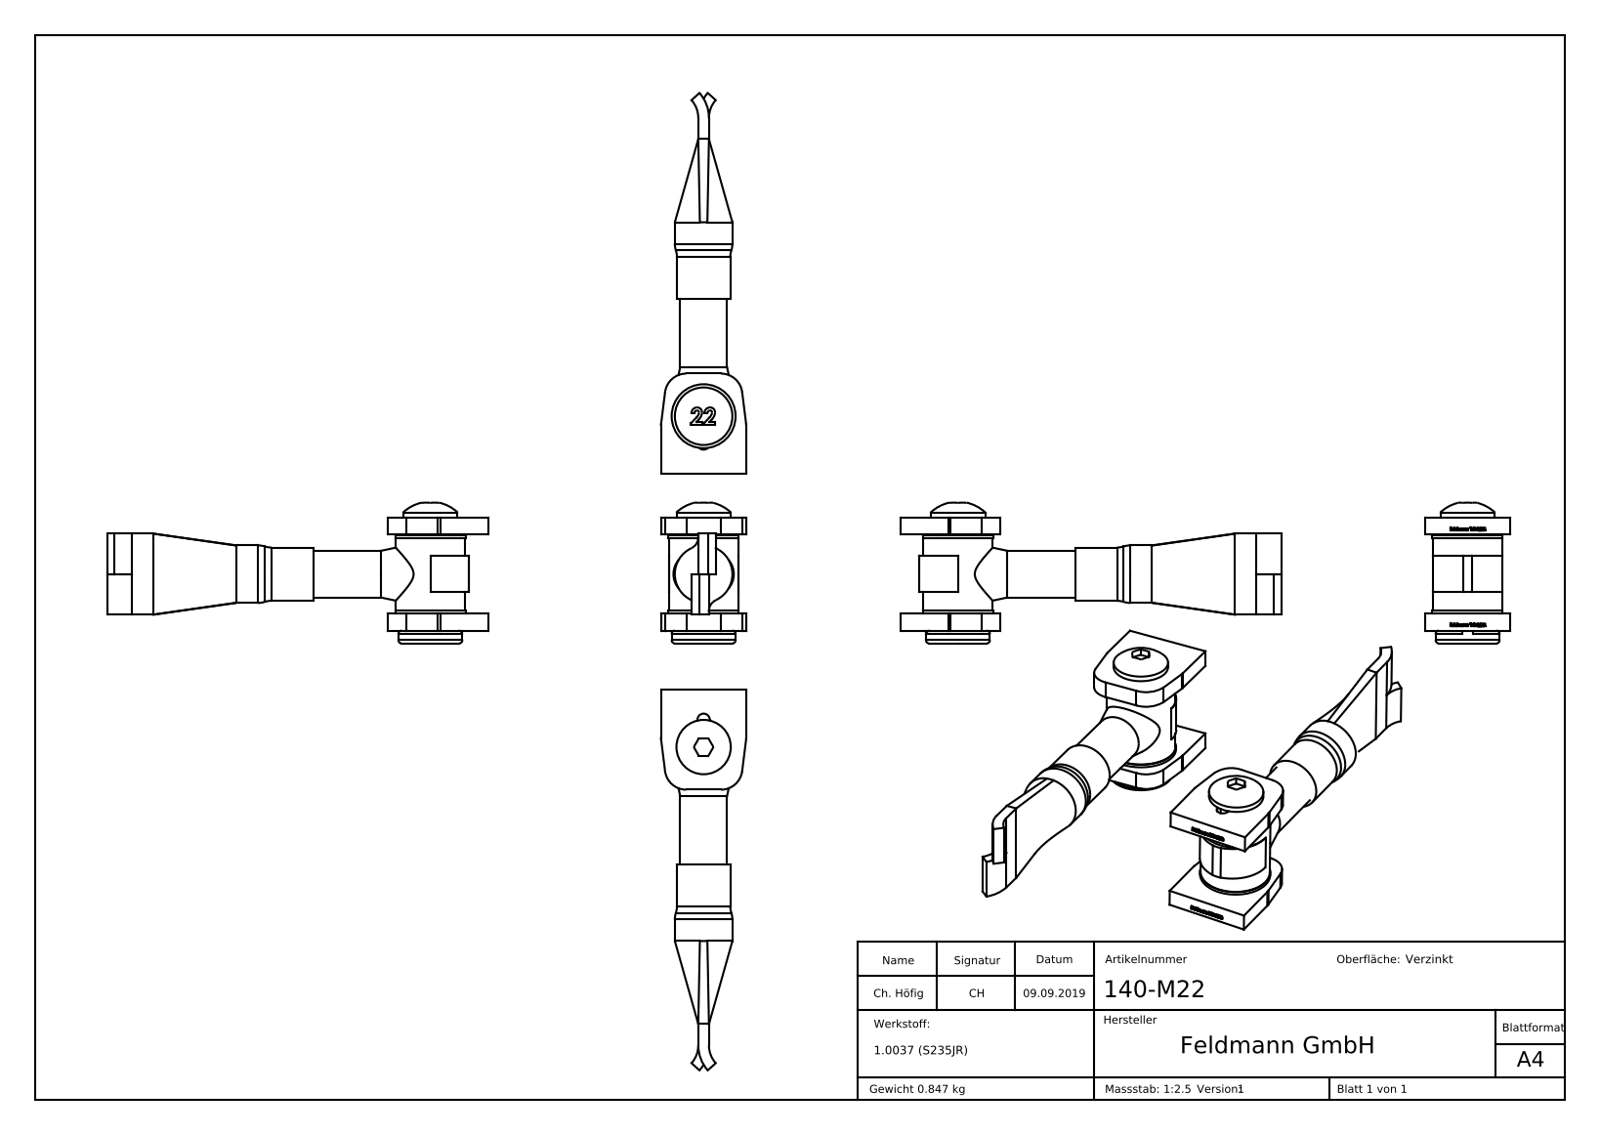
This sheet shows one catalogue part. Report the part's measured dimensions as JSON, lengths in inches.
{"part_name": "140-MXX Teil5_140-M22 Teil5; 140-MXX Teil1_140-M22 Teil1; 140-MXX Teil2_140-M22 Teil2; 140-M22 (+3 more)", "step_written_by": "SolidWorks 2015 (CONFIG_CONTROL_DESIGN)", "units": "inches", "bodies": {"solids": 8, "faces": 564, "planar": 317, "cylindrical": 61, "other": 186}, "overall_size": [6.969, 2.601, 1.575], "volume_in3": 6.681, "surface_area_in2": 68.02, "round_holes": [[0.335, 1], [0.472, 1], [0.669, 1], [0.768, 1], [0.787, 1], [0.795, 1], [0.866, 1]], "round_bosses_or_shafts": [[1.299, 1], [1.28, 1], [1.181, 1], [1.063, 1], [1.004, 1], [0.984, 1], [0.866, 1], [0.768, 1]], "partial_cylinders_radius": [[0.394, 5], [0.312, 2], [0.509, 2], [0.709, 2], [0.114, 1]], "face_to_face_distances": [0.315, 1.772, 0.374, 1.713, 0.059, 1.398, 2.087, 1.457, 1.339, 0.055]}
